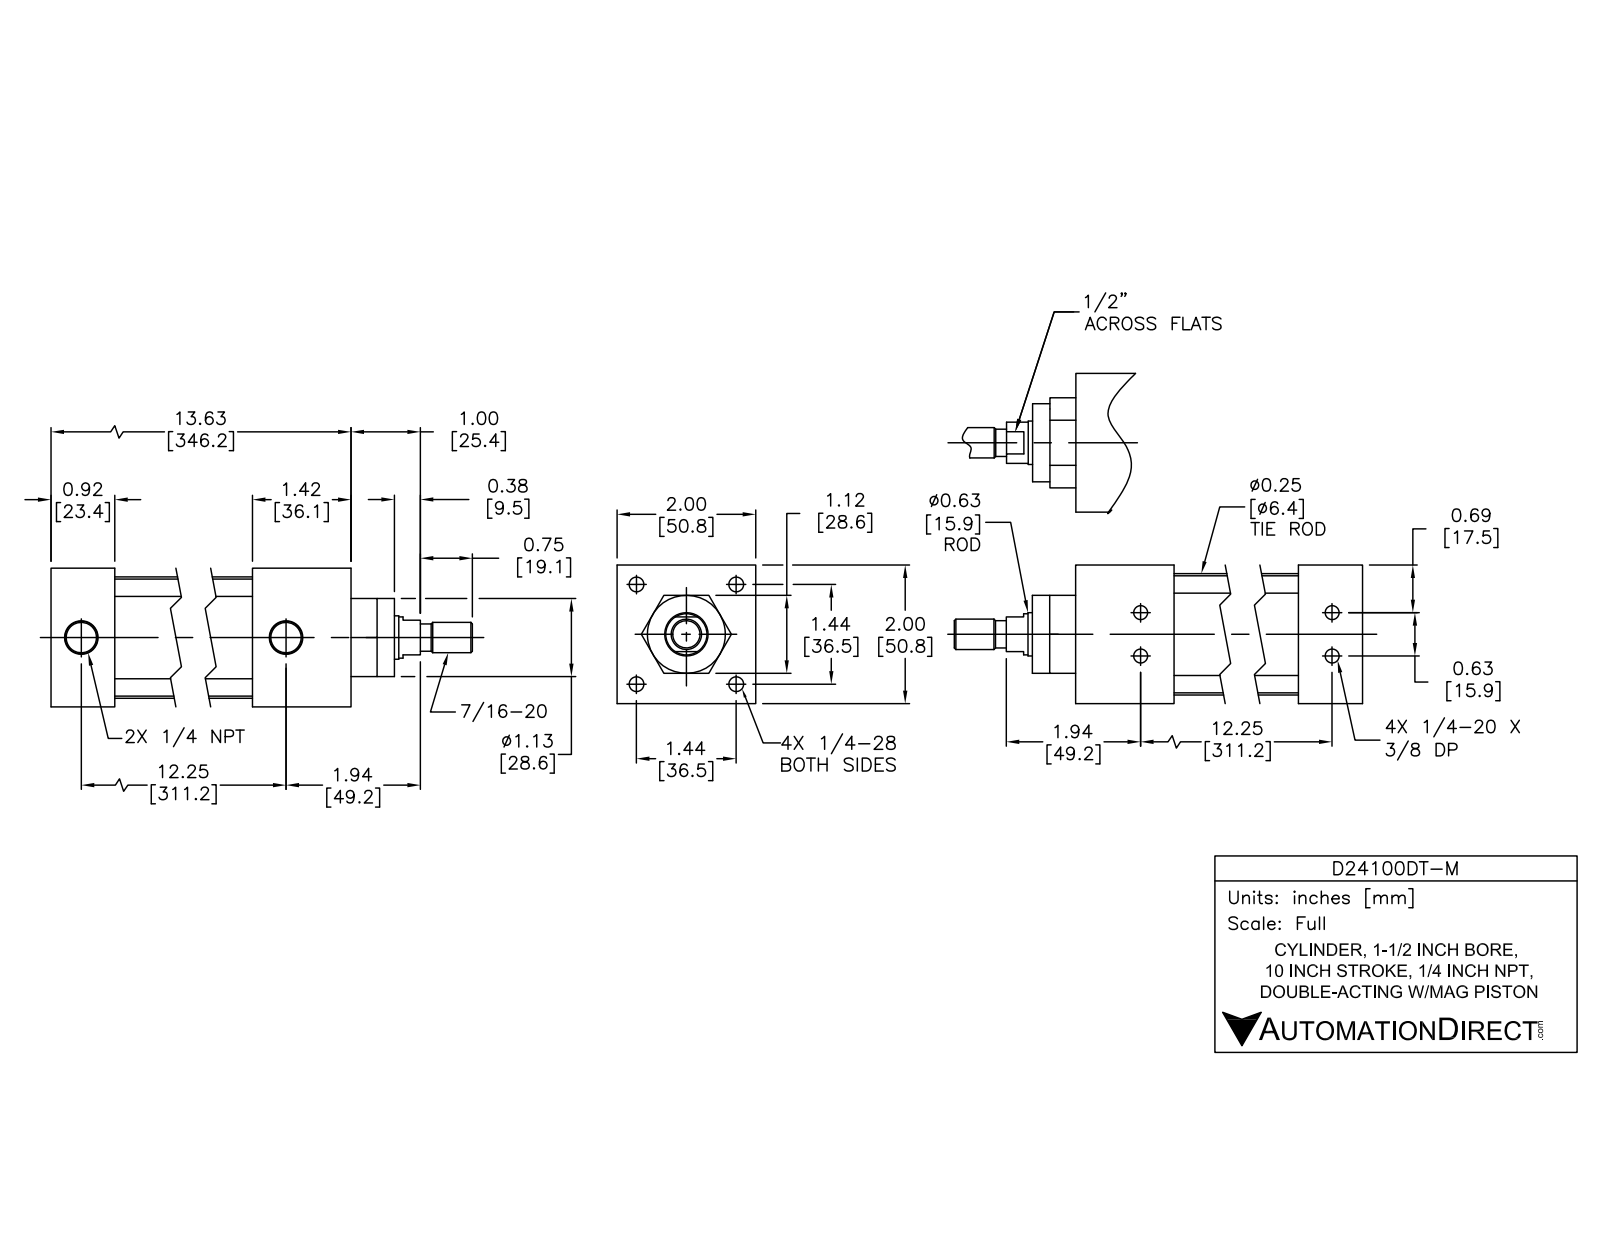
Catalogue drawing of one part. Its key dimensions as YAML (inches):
part_name: "D24100DT-M; D24100DT-M BODY; D24100DT-M PISTON"
step_written_by: "SolidWorks 2015 (AUTOMOTIVE_DESIGN)"
units: inches
bodies: {solids: 12, faces: 303, planar: 99, cylindrical: 114, other: 90}
overall_size: [15.371, 2, 2]
volume: 23.66
surface_area: 242.6
round_holes:
  - {diameter: 0.196, count: 4}
  - {diameter: 0.211, count: 4}
  - {diameter: 0.281, count: 4}
  - {diameter: 0.406, count: 4}
  - {diameter: 0.297, count: 2}
  - {diameter: 0.477, count: 2}
  - {diameter: 0.625, count: 1}
  - {diameter: 0.628, count: 1}
  - {diameter: 1.5, count: 1}
round_bosses_or_shafts:
  - {diameter: 0.39, count: 4}
  - {diameter: 0.25, count: 4}
  - {diameter: 0.222, count: 4}
  - {diameter: 1.75, count: 1}
  - {diameter: 1.497, count: 1}
  - {diameter: 1.121, count: 1}
  - {diameter: 0.622, count: 1}
  - {diameter: 0.59, count: 1}
partial_cylinders:
  - {radius: 0.2, count: 4}
face_to_face_distances: [2, 13.621, 1.42, 12.201, 12.701, 11.281, 0.92, 1.121, 12.601, 11.181]
hole_center_spacings: [0.313, 1.014, 1.434, 0.625, 2.028, 12.247, 12.25, 12.25]
